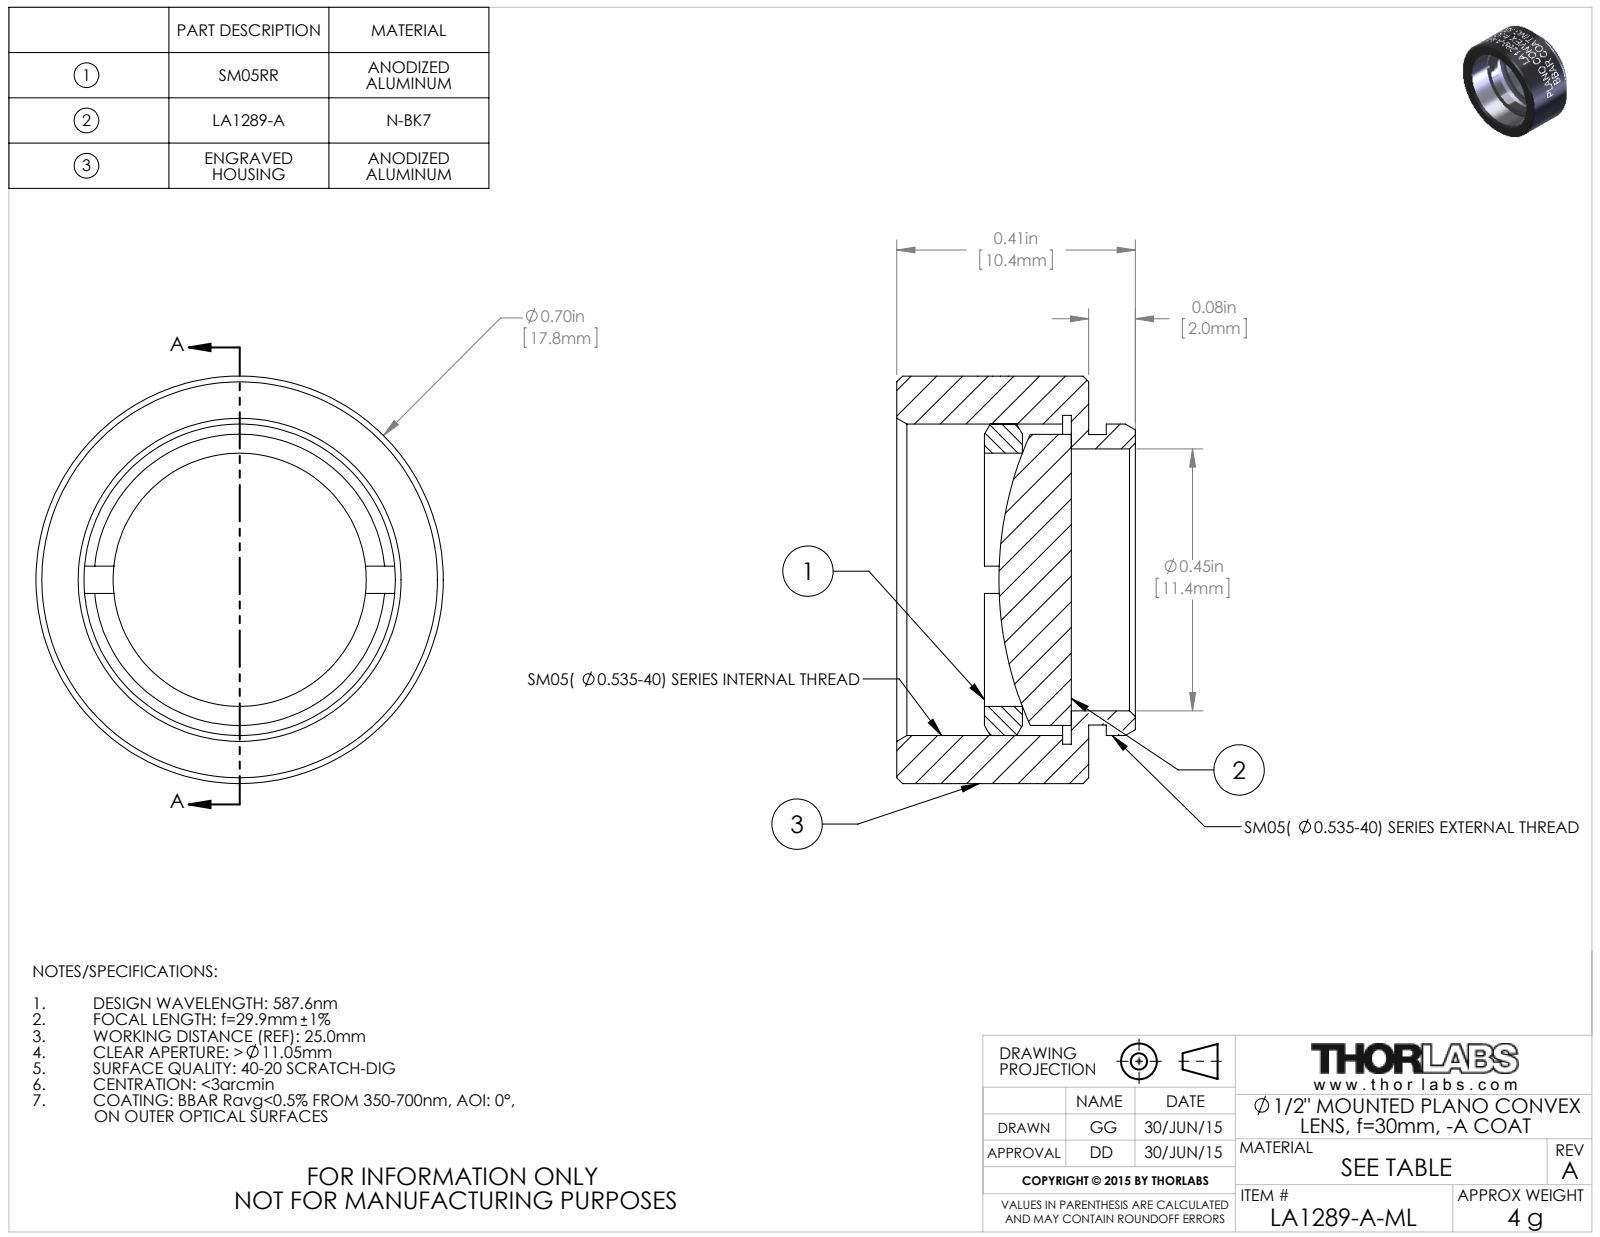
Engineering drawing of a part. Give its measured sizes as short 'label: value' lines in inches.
name: TTN039549-E0W
written by: SolidWorks 2014 (CONFIG_CONTROL_DESIGN)
unit: in
bodies: 3 solids, 141 faces (16 planar, 108 cylindrical, 17 other)
size: 0.7 × 0.7 × 0.41
volume: 0.082 in³; area: 2.86 in²
holes: 1× ⌀0.435, 1× ⌀0.45, 1× ⌀0.535, 1× ⌀0.565
bosses: 1× ⌀0.7, 1× ⌀0.535, 1× ⌀0.5, 1× ⌀0.499
face distances: 0.03, 0.33, 0.3, 0.115, 0.084, 0.216, 0.18, 0.149, 0.065, 0.151
